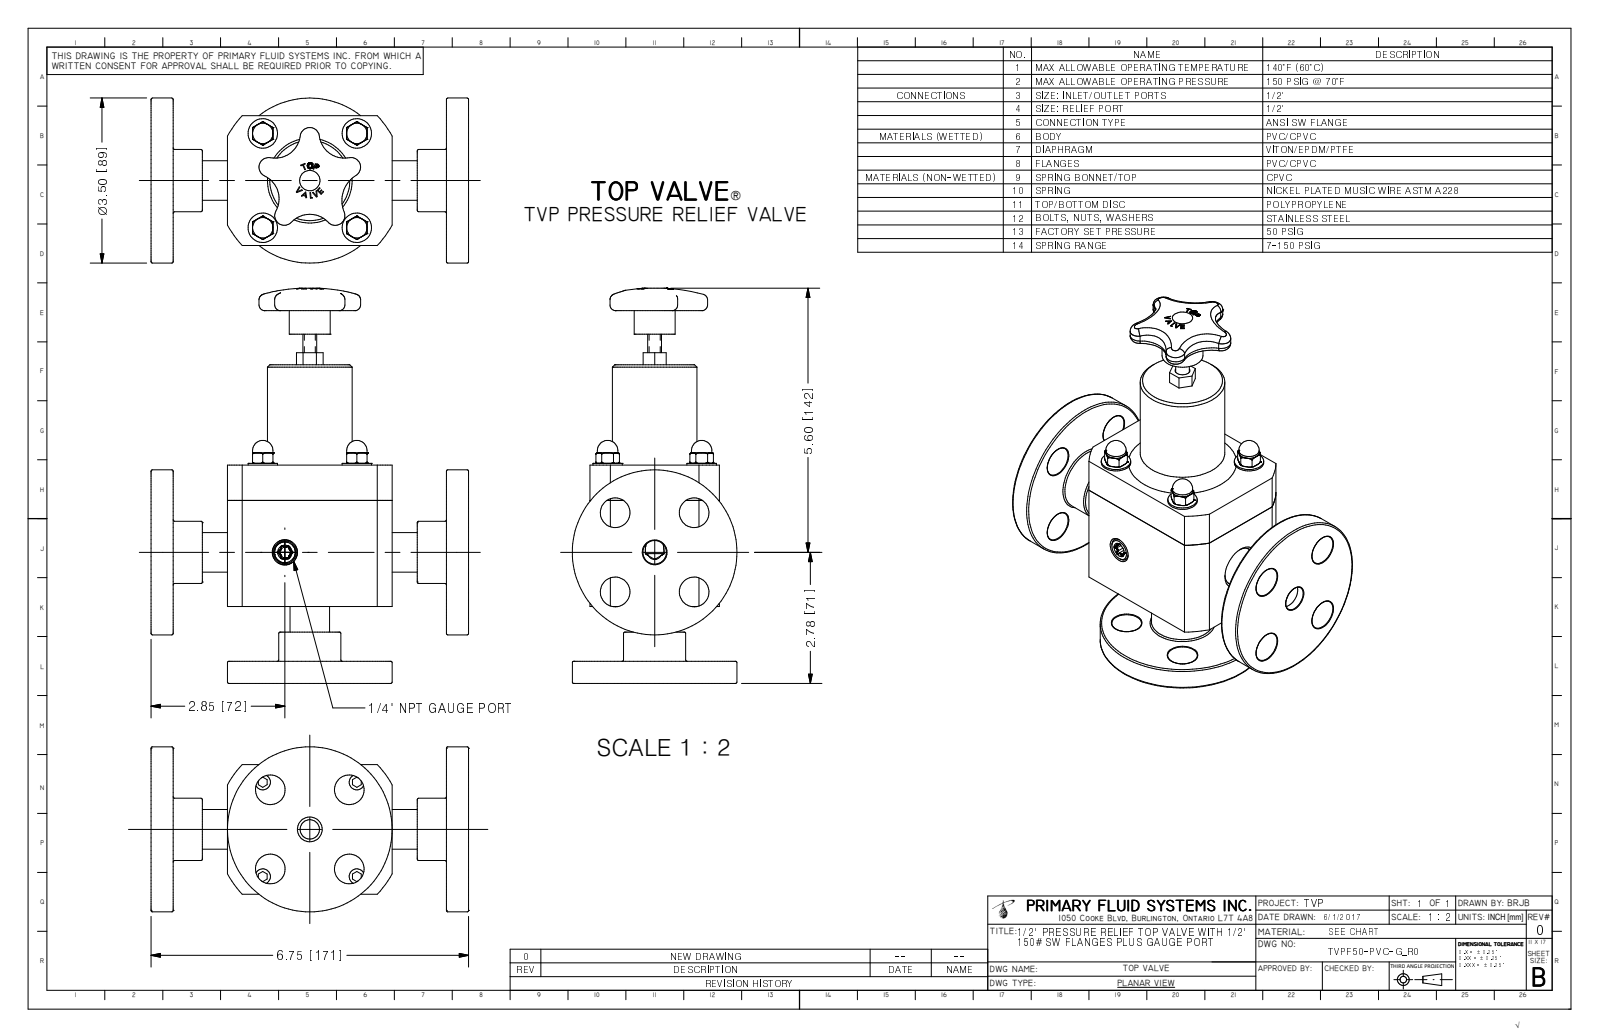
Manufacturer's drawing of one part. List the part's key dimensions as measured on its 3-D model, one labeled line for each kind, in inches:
Part name (STEP PRODUCT): TVPF50-PVC-G_R0
STEP written by: Autodesk Inventor 2009 (AUTOMOTIVE_DESIGN)
Units: inches
Bodies: 1 solid, 438 faces (168 planar, 68 cylindrical, 202 other)
Overall size (bounding box): 8.38 × 6.75 × 3.5
Volume: 48.78 in³ · Surface area: 190.5 in²
Round holes (diameter × count): ⌀0.63 ×8, ⌀0.175 ×4, ⌀0.526 ×2, ⌀2.4 ×1
Round bosses / shafts (diameter × count): ⌀0.625 ×4, ⌀0.433 ×4, ⌀3.5 ×2, ⌀1.32 ×2, ⌀2.375 ×1, ⌀1.8 ×1, ⌀0.87 ×1, ⌀0.293 ×1
Partial cylindrical surfaces — rounded edges, fillets, slot ends (radius × count): R0.027 ×6, R0.085 ×5, R0.205 ×5, R0.536 ×4, R0.656 ×4, R0.625 ×1, R0.745 ×1, R1.988 ×1
Main face-to-face distances: 0.47, 6.28, 5.125, 1.625, 1.155, 4.655, 2.75, 1.63, 6.75, 1.16
Hole centre spacings: 1.188, 1.68, 1.847, 0.227, 1.414, 2, 2.375, 2.602
